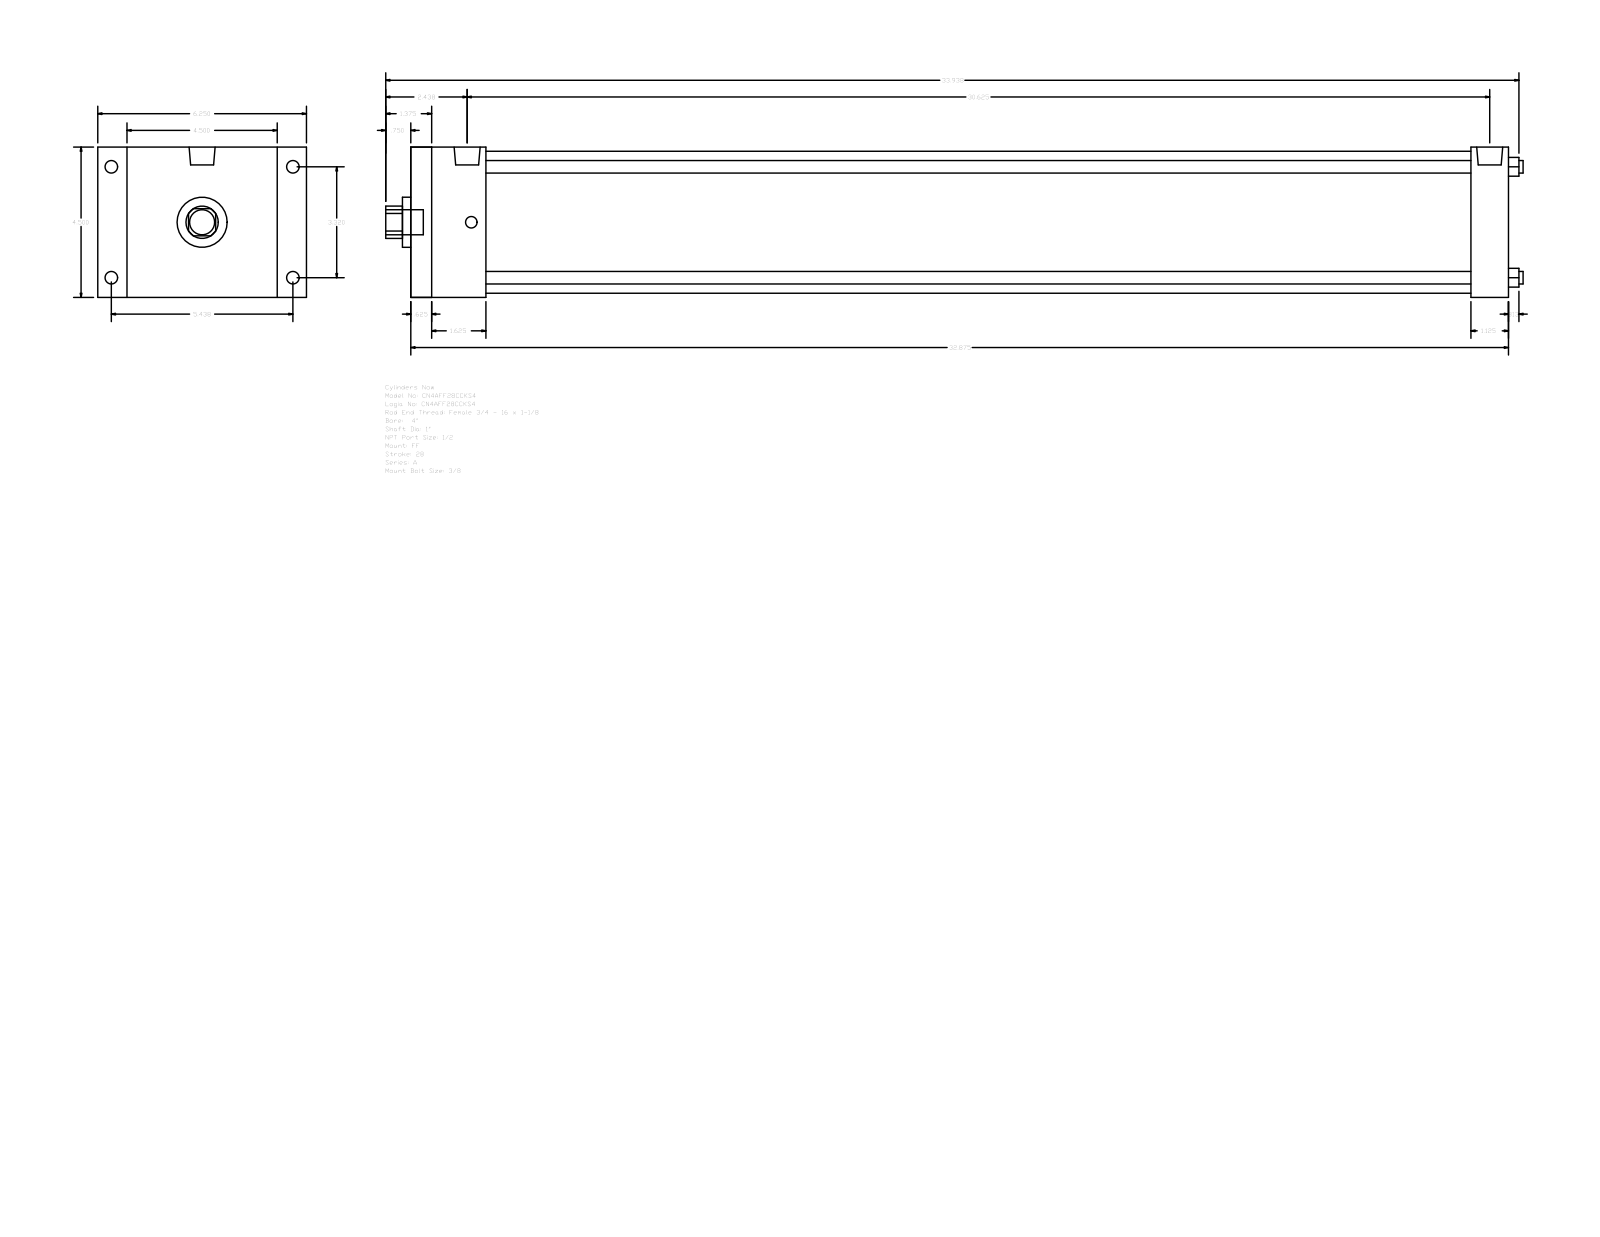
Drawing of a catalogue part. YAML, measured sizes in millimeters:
part_name: "A_FF__0400_1"
step_written_by: "GSSL Pune (CONFIG_CONTROL_DESIGN)"
units: millimeters
bodies: {solids: 0, faces: 92, planar: 64, cylindrical: 28, other: 0}
overall_size: [865.19, 158.75, 114.3]
round_holes:
  - {diameter: 9.53, count: 4}
  - {diameter: 25.4, count: 1}
  - {diameter: 38.1, count: 1}
  - {diameter: 107.95, count: 1}
round_bosses_or_shafts:
  - {diameter: 9.53, count: 4}
  - {diameter: 8.73, count: 4}
  - {diameter: 19.77, count: 2}
  - {diameter: 19.05, count: 1}
partial_cylinders:
  - {radius: 12.29, count: 1}
face_to_face_distances: [114.3, 835.03, 15.87, 819.16, 22.23, 136.53, 806.45, 790.58, 28.58, 57.15]
hole_center_spacings: [59.62, 84.32, 119.25]
